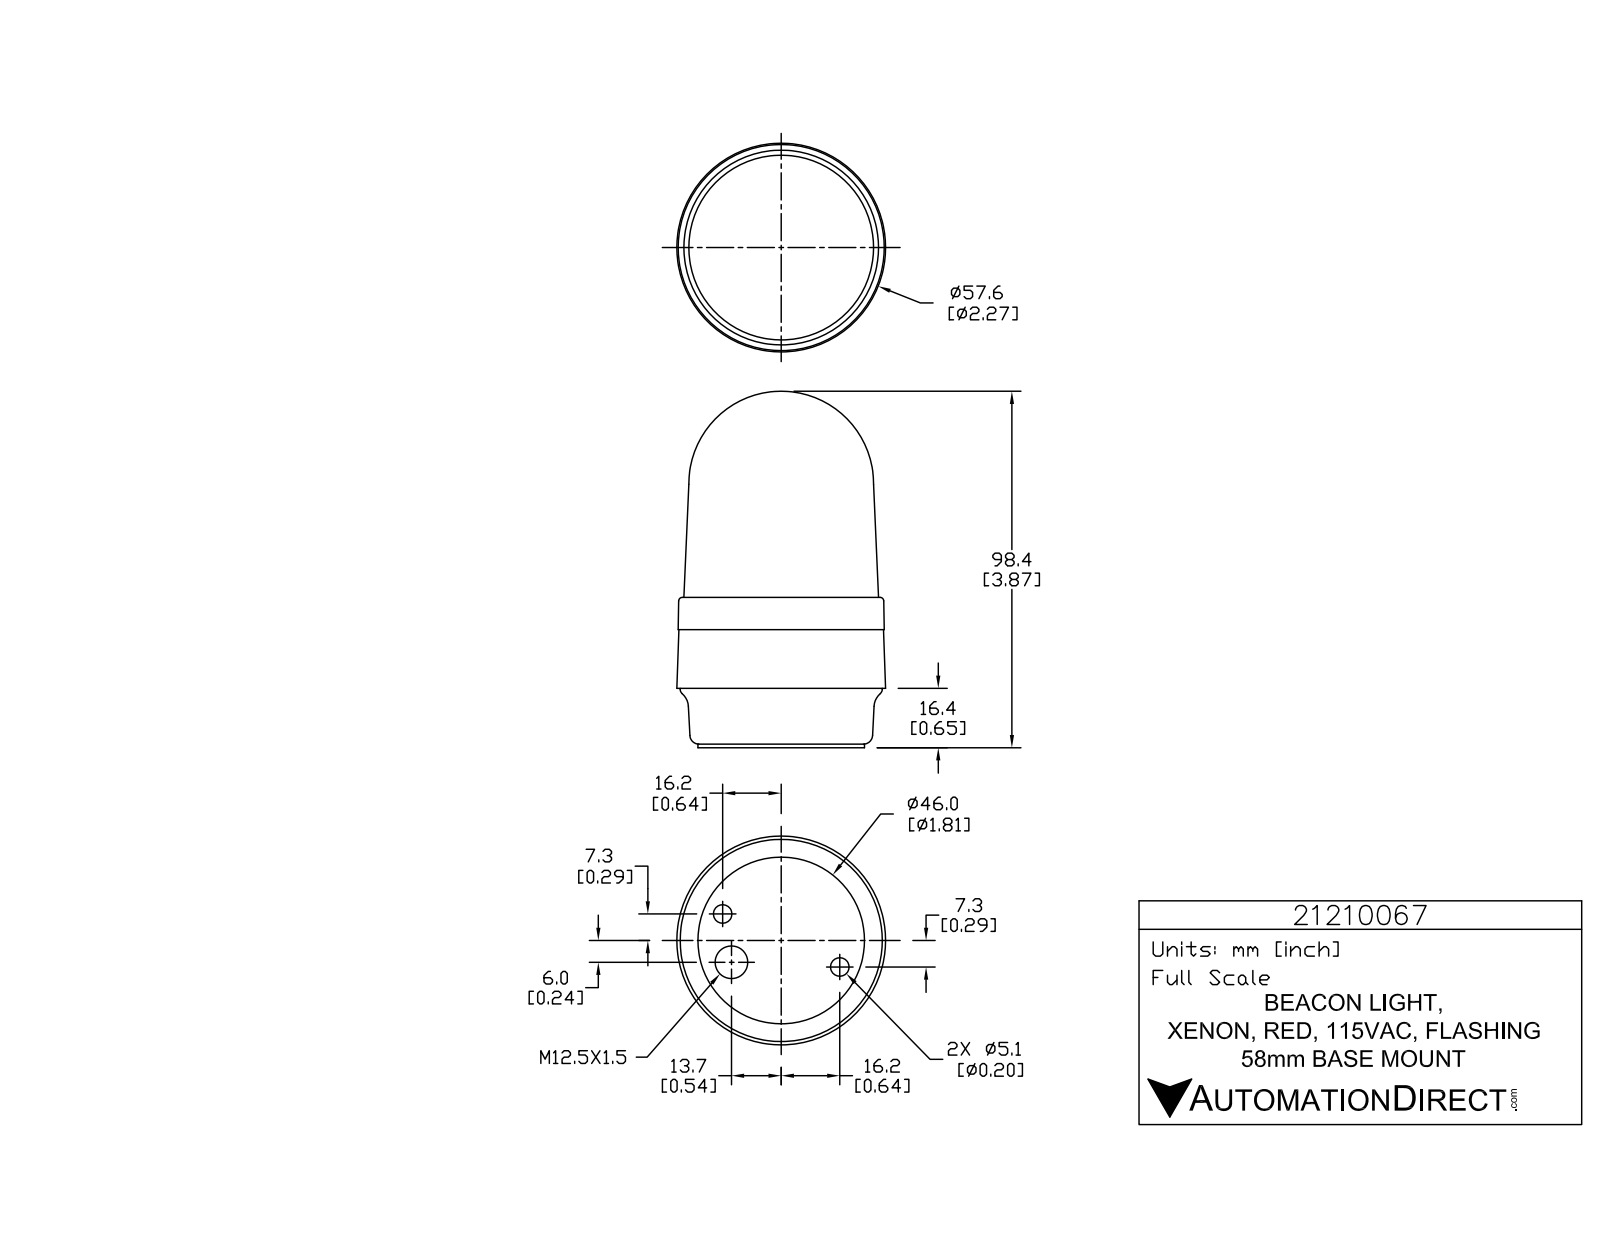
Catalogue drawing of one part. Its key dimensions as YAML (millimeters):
part_name: "21210067"
step_written_by: "SolidWorks 2015 (AUTOMOTIVE_DESIGN)"
units: millimeters
bodies: {solids: 1, faces: 764, planar: 527, cylindrical: 145, other: 92}
overall_size: [98.4, 57.63, 57.63]
volume: 199898
surface_area: 18922
round_holes:
  - {diameter: 0.99, count: 3}
  - {diameter: 5.11, count: 2}
  - {diameter: 9, count: 1}
round_bosses_or_shafts:
  - {diameter: 5.74, count: 3}
  - {diameter: 1.43, count: 3}
  - {diameter: 55.8, count: 1}
  - {diameter: 46, count: 1}
partial_cylinders:
  - {radius: 0.2, count: 6}
  - {radius: 0.21, count: 6}
  - {radius: 0.21, count: 6}
  - {radius: 3.32, count: 6}
  - {radius: 0.1, count: 3}
  - {radius: 0.12, count: 3}
  - {radius: 0.19, count: 3}
  - {radius: 0.2, count: 3}
face_to_face_distances: [16.4, 1, 15.4, 41.5, 40.5, 25.1, 32.6, 31.6, 16.2, 8.9]
hole_center_spacings: [13.56, 29.94, 35.5]
